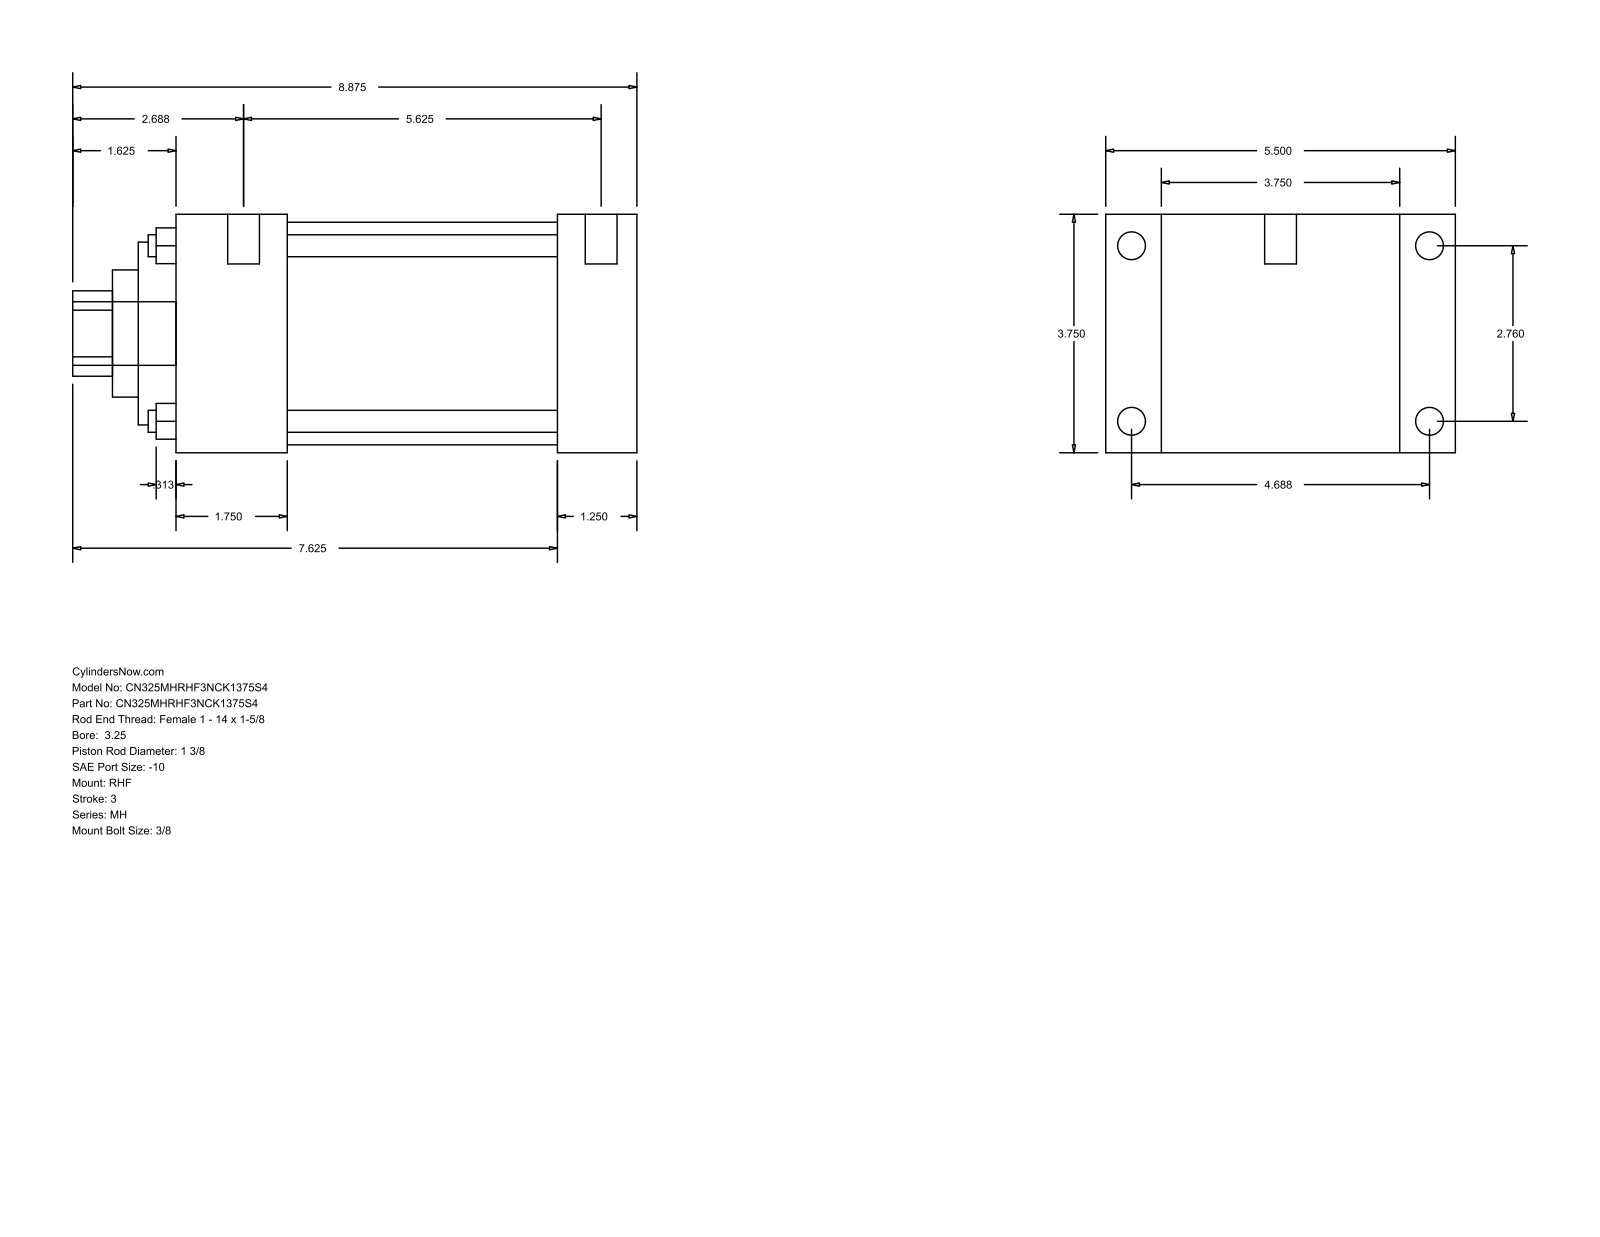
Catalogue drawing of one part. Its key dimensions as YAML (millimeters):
part_name: "MH_RHF__0325_1.375"
step_written_by: "GSSL Pune (CONFIG_CONTROL_DESIGN)"
units: millimeters
bodies: {solids: 0, faces: 90, planar: 61, cylindrical: 29, other: 0}
overall_size: [225.43, 139.7, 95.25]
round_holes:
  - {diameter: 8.76, count: 4}
  - {diameter: 34.92, count: 1}
  - {diameter: 50.8, count: 1}
  - {diameter: 73.03, count: 1}
  - {diameter: 88.9, count: 1}
round_bosses_or_shafts:
  - {diameter: 11.13, count: 4}
  - {diameter: 5.56, count: 4}
  - {diameter: 12.7, count: 2}
  - {diameter: 25.4, count: 1}
partial_cylinders:
  - {radius: 17.06, count: 1}
face_to_face_distances: [95.24, 31.75, 22.23, 117.47, 152.41, 184.16, 139.7, 44.45, 107.96, 139.71]
hole_center_spacings: [49.57, 70.1, 99.14]
